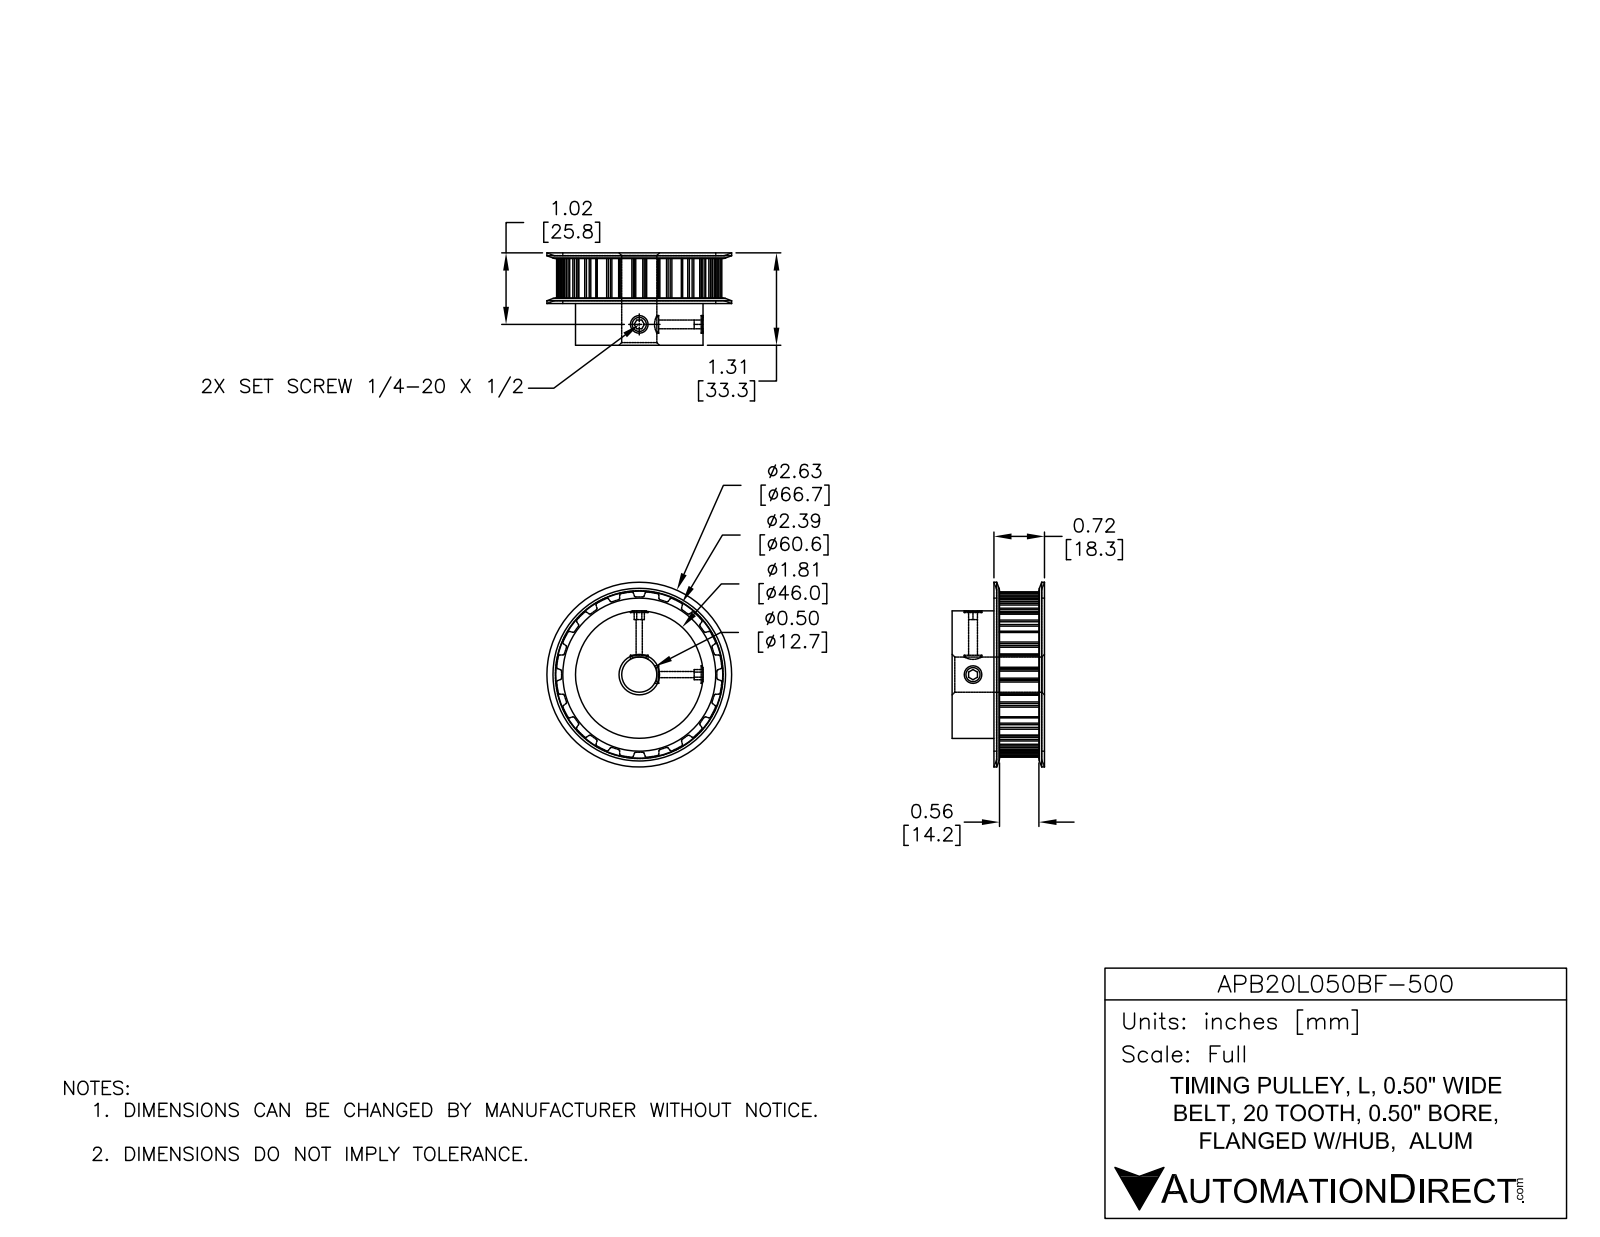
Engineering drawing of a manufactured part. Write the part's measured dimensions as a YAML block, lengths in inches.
part_name: "APB20L050BF-500"
step_written_by: "SolidWorks 2014 (AUTOMOTIVE_DESIGN)"
units: inches
bodies: {solids: 1, faces: 166, planar: 66, cylindrical: 78, other: 22}
overall_size: [2.625, 2.625, 1.313]
volume: 4.308
surface_area: 24.36
round_holes:
  - {diameter: 0.088, count: 2}
  - {diameter: 0.5, count: 1}
round_bosses_or_shafts:
  - {diameter: 1.813, count: 1}
partial_cylinders:
  - {radius: 0.015, count: 40}
  - {radius: 1.124, count: 1}
face_to_face_distances: [1.313, 0.04, 1.273, 0.68, 0.64, 0.633, 2.357, 2.357, 0.907, 0.04]
